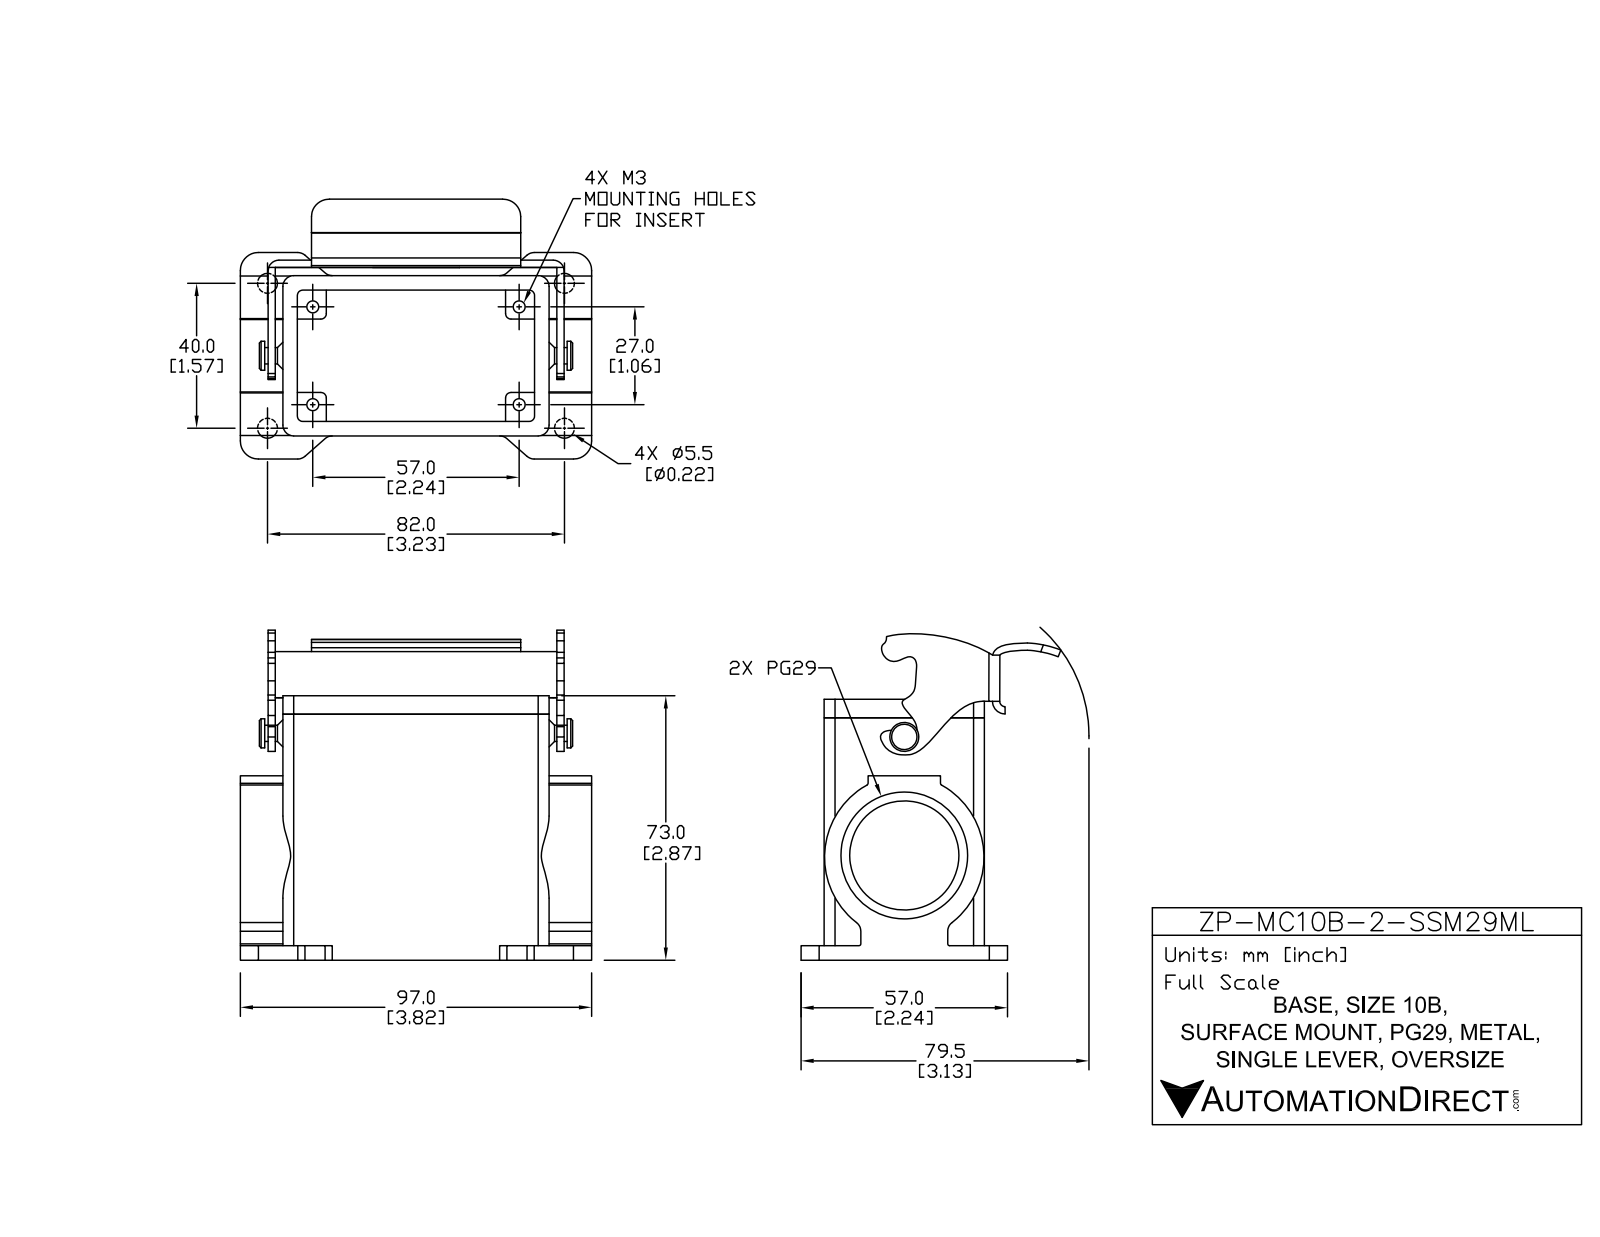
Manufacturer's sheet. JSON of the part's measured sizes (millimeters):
{"part_name": "ZP-MC10B-2-SSM29ML", "step_written_by": "SolidWorks 2011 (AUTOMOTIVE_DESIGN)", "units": "millimeters", "bodies": {"solids": 3, "faces": 261, "planar": 109, "cylindrical": 144, "other": 8}, "overall_size": [97, 86.17, 76.78], "volume_mm3": 109925, "surface_area_mm2": 53561, "round_holes": [[3, 4], [5.5, 4], [30.17, 1], [35, 1]], "round_bosses_or_shafts": [[8, 1], [4.5, 1]], "partial_cylinders_radius": [[0.5, 17], [3, 15], [1.5, 8], [5, 5], [2, 3], [4, 3], [1, 2], [10, 2]], "face_to_face_distances": [4, 44.24, 40.24, 40.25, 36.25, 3.99, 57.5, 8.5, 1.15, 71], "hole_center_spacings": [15.12, 15.55, 27, 37.64, 38.34, 44.75, 57.5, 63.52]}
